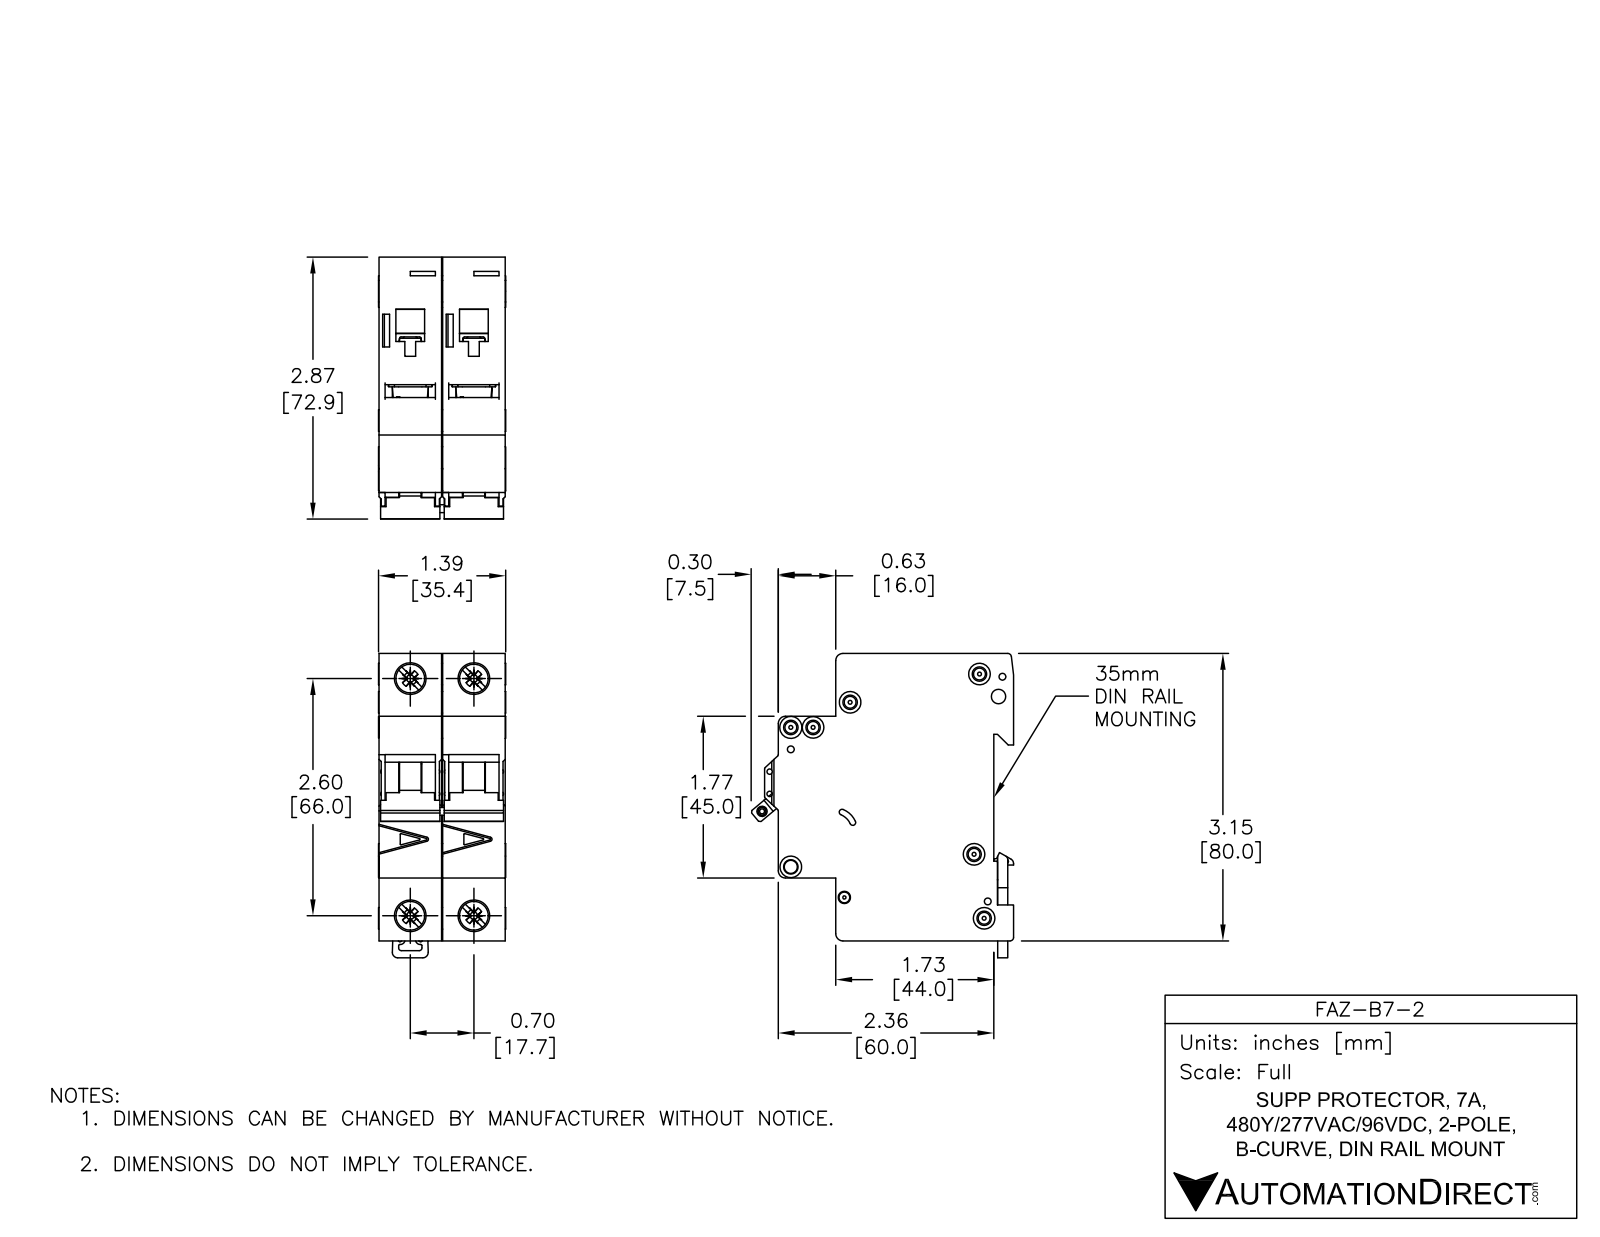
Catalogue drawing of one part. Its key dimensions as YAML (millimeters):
part_name: "FAZ-B7-2"
step_written_by: "SolidWorks 2014 (AUTOMOTIVE_DESIGN)"
units: millimeters
bodies: {solids: 8, faces: 1104, planar: 466, cylindrical: 396, other: 242}
overall_size: [84.78, 73.04, 35.4]
volume: 149808
surface_area: 38799
round_holes:
  - {diameter: 3.6, count: 6}
  - {diameter: 1.9, count: 3}
  - {diameter: 1.09, count: 2}
  - {diameter: 1.5, count: 2}
  - {diameter: 4, count: 2}
  - {diameter: 7.15, count: 2}
  - {diameter: 8.2, count: 2}
  - {diameter: 2.15, count: 1}
  - {diameter: 2.2, count: 1}
  - {diameter: 2.55, count: 1}
  - {diameter: 3.3, count: 1}
  - {diameter: 3.4, count: 1}
round_bosses_or_shafts:
  - {diameter: 6, count: 4}
  - {diameter: 8.2, count: 2}
  - {diameter: 2.5, count: 2}
partial_cylinders:
  - {radius: 0.25, count: 49}
  - {radius: 0.5, count: 19}
  - {radius: 2, count: 10}
  - {radius: 0.2, count: 8}
  - {radius: 1, count: 8}
  - {radius: 0.8, count: 2}
  - {radius: 1.8, count: 2}
  - {radius: 3, count: 2}
face_to_face_distances: [17.7, 17.5, 35.2, 79.48, 5.5, 49.5, 44, 65.5, 60, 16]
hole_center_spacings: [6.2, 13.64, 17.7, 66, 68.33, 4.81, 5.19, 5.61]
